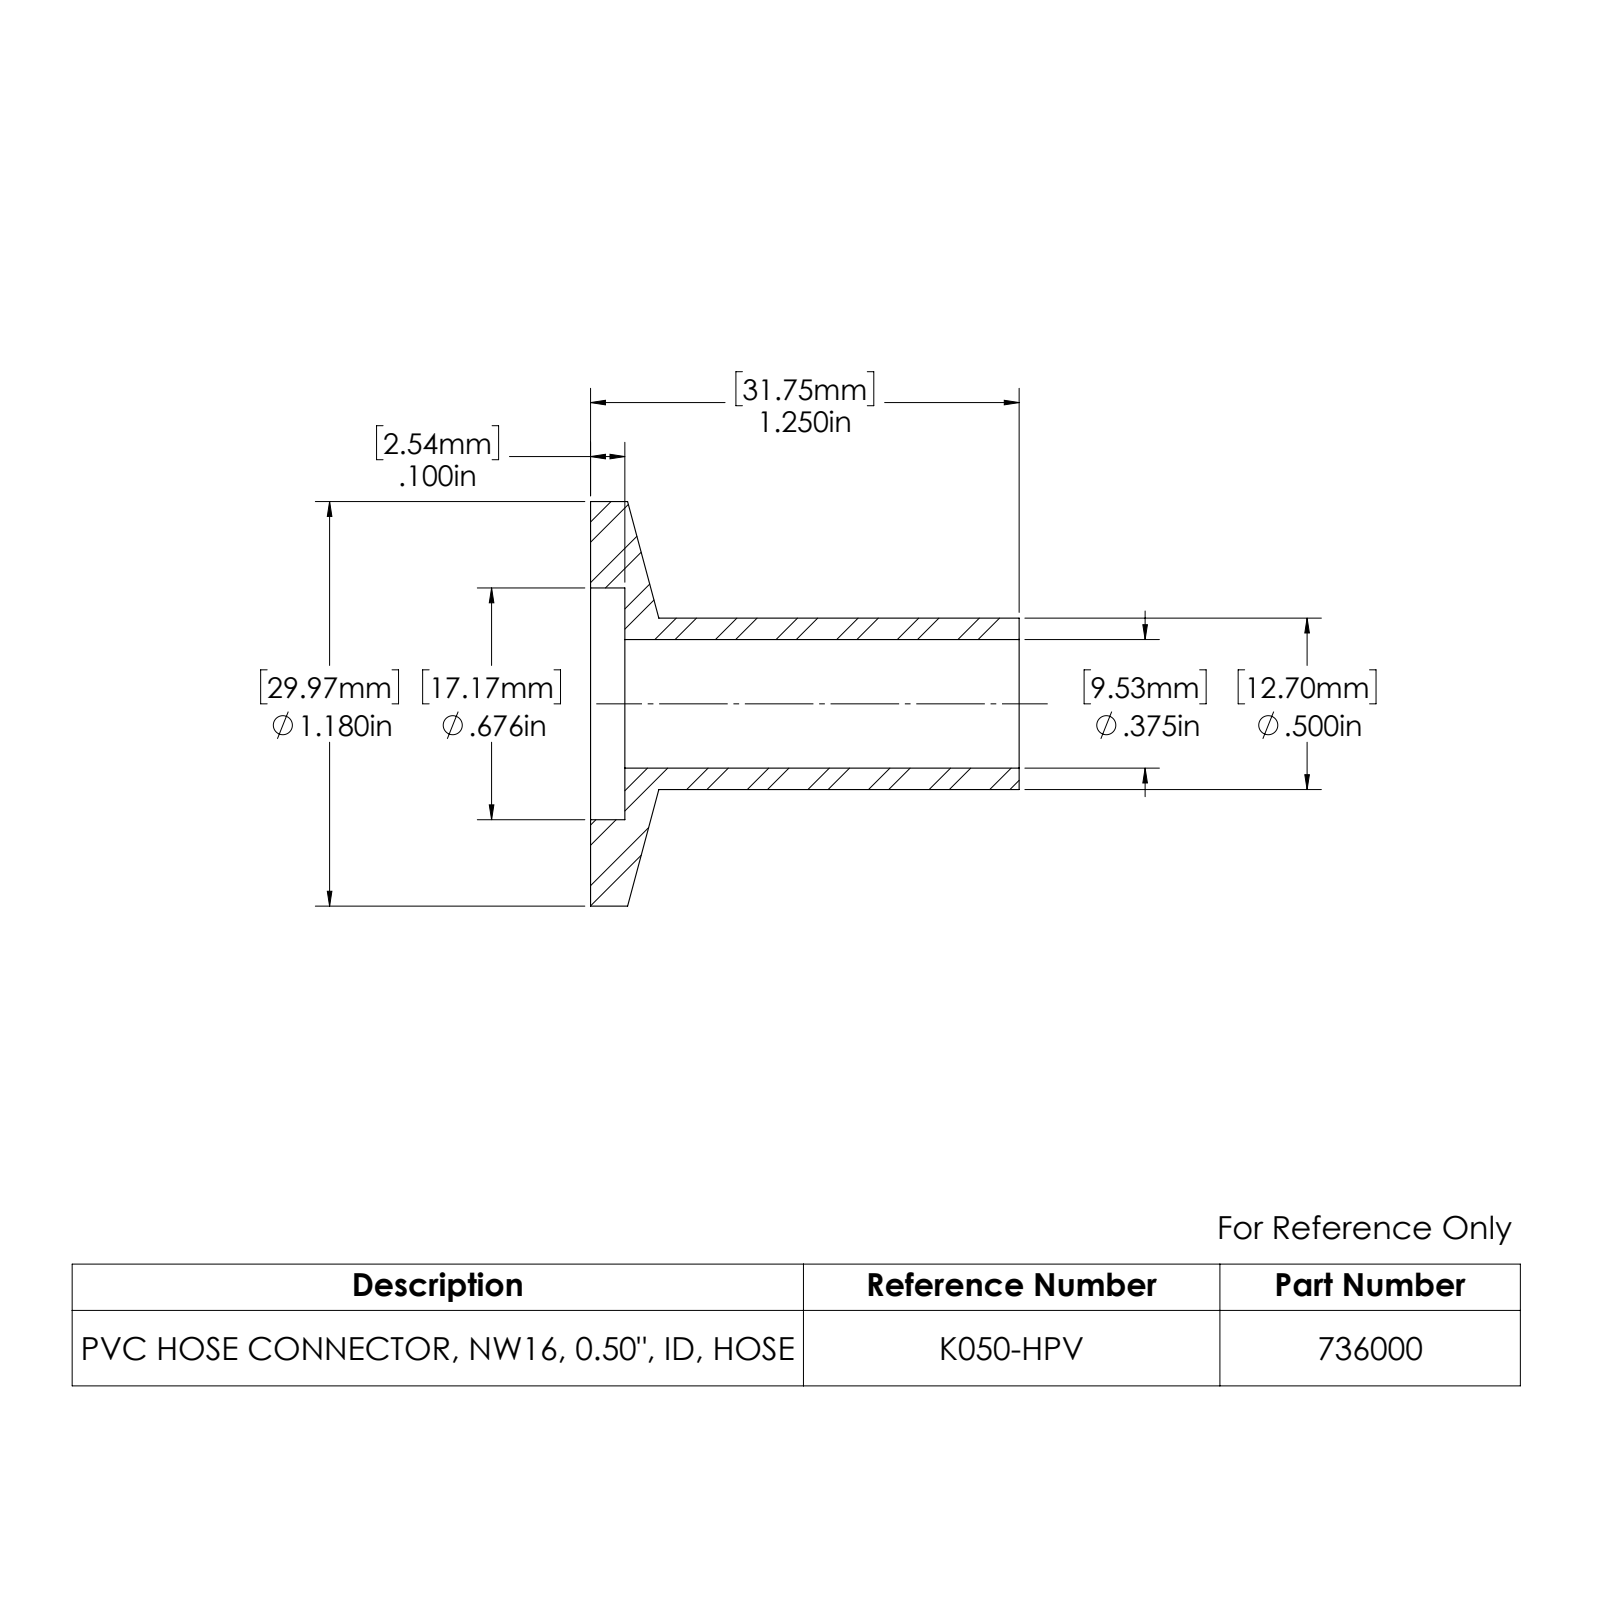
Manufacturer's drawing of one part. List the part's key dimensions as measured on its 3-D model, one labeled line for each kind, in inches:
Part name (STEP PRODUCT): 736000
STEP written by: SolidWorks 2022 (AUTOMOTIVE_DESIGN)
Units: inches
Bodies: 1 solid, 13 faces (3 planar, 8 cylindrical, 2 other)
Overall size (bounding box): 1.25 × 1.18 × 1.18
Volume: 0.215 in³ · Surface area: 5.616 in²
Round holes (diameter × count): ⌀0.375 ×1, ⌀0.676 ×1
Round bosses / shafts (diameter × count): ⌀1.18 ×1, ⌀0.5 ×1
Main face-to-face distances: 0.1, 1.15, 1.25
